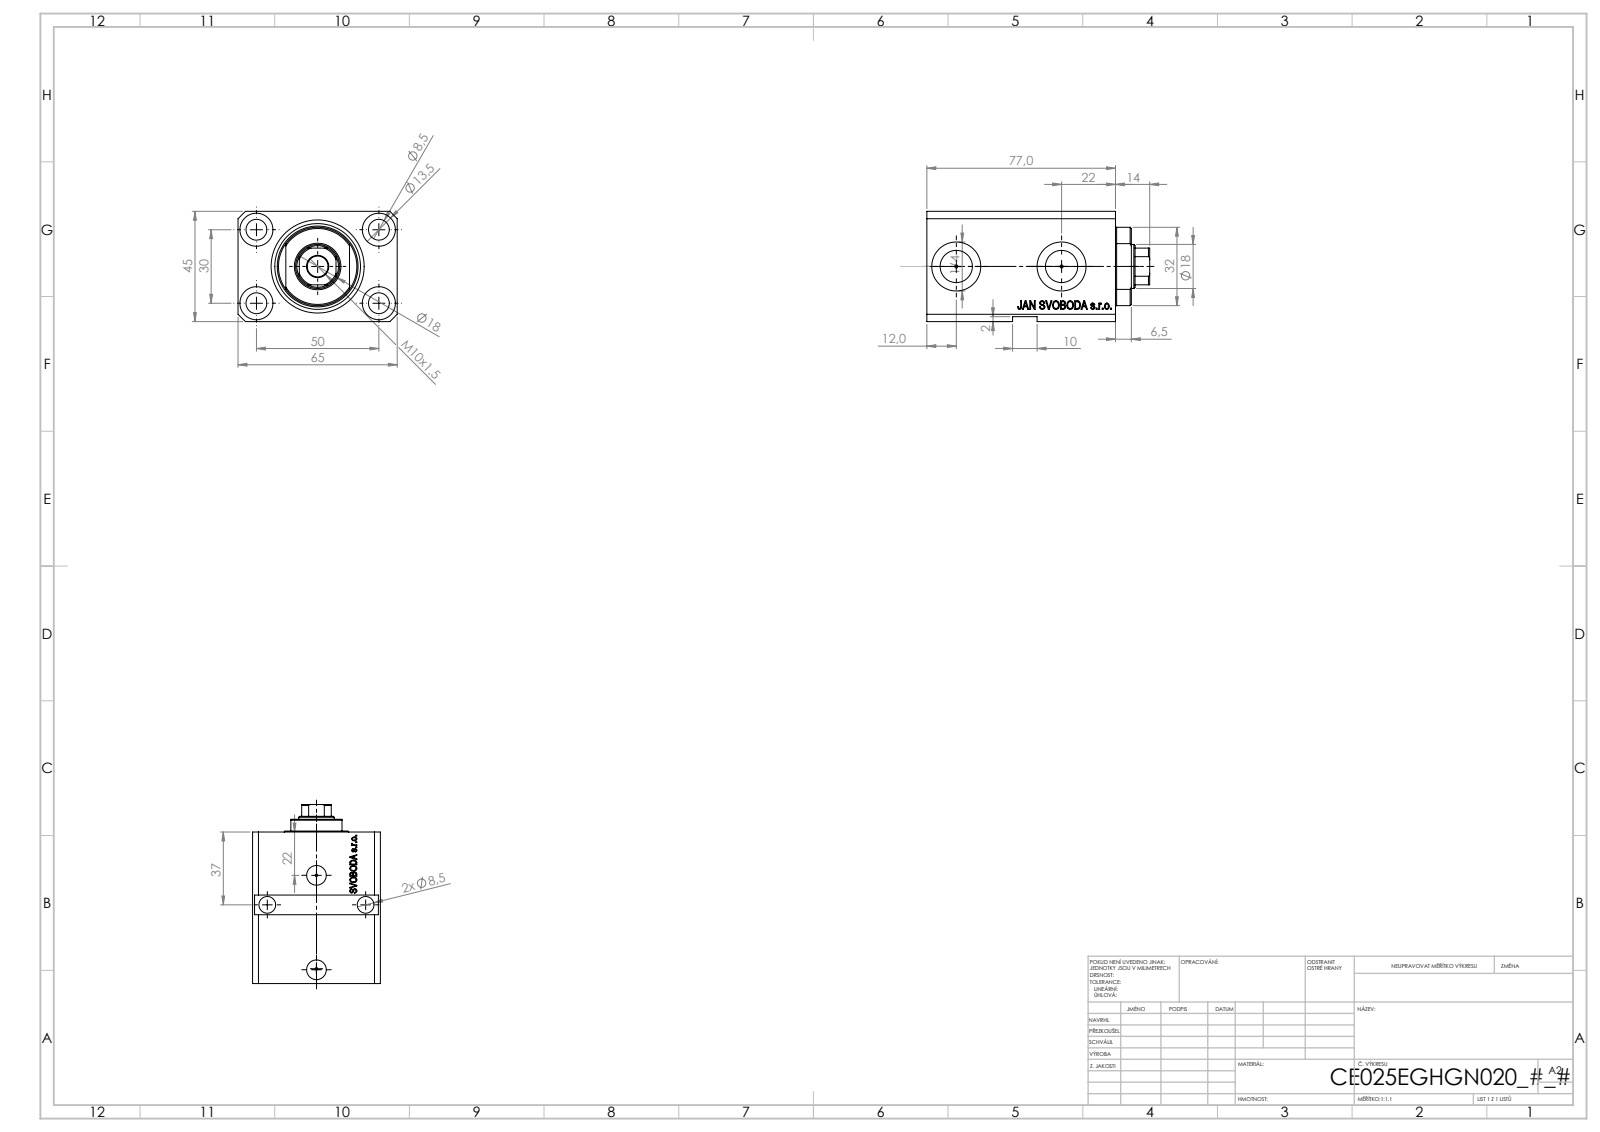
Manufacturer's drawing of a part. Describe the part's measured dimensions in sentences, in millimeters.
The part is named "V250CE_C_VCP; V250CE_E_Body; V250CE_VC_E". Its 3-D file was written by "SolidWorks 2019 (CONFIG_CONTROL_DESIGN)". It is 3 solids with 897 faces: 435 planar, 84 cylindrical and 378 other. Overall it measures 91 by 65 by 45 millimeters. Its volume is 191 714 cubic millimeters and its surface area 52 259 square millimeters. Round holes: 7 of diameter 8.5, 4 of diameter 1.25, 4 of diameter 13.5, 2 of diameter 10, 2 of diameter 13.16, 2 of diameter 20, 1 of diameter 18, 1 of diameter 25, 1 of diameter 38. Partial cylindrical surfaces (rounded edges, fillets, slot ends): 1 of radius 8.5, 1 of radius 16. The main face-to-face distances are 45, 65, 63, 14, 77, 6.9, 56.1, 70.1, 43, 9. The hole center spacings are 29.15, 50, 30, 40.98, 41.4, 58.31, 0.53, 43.
